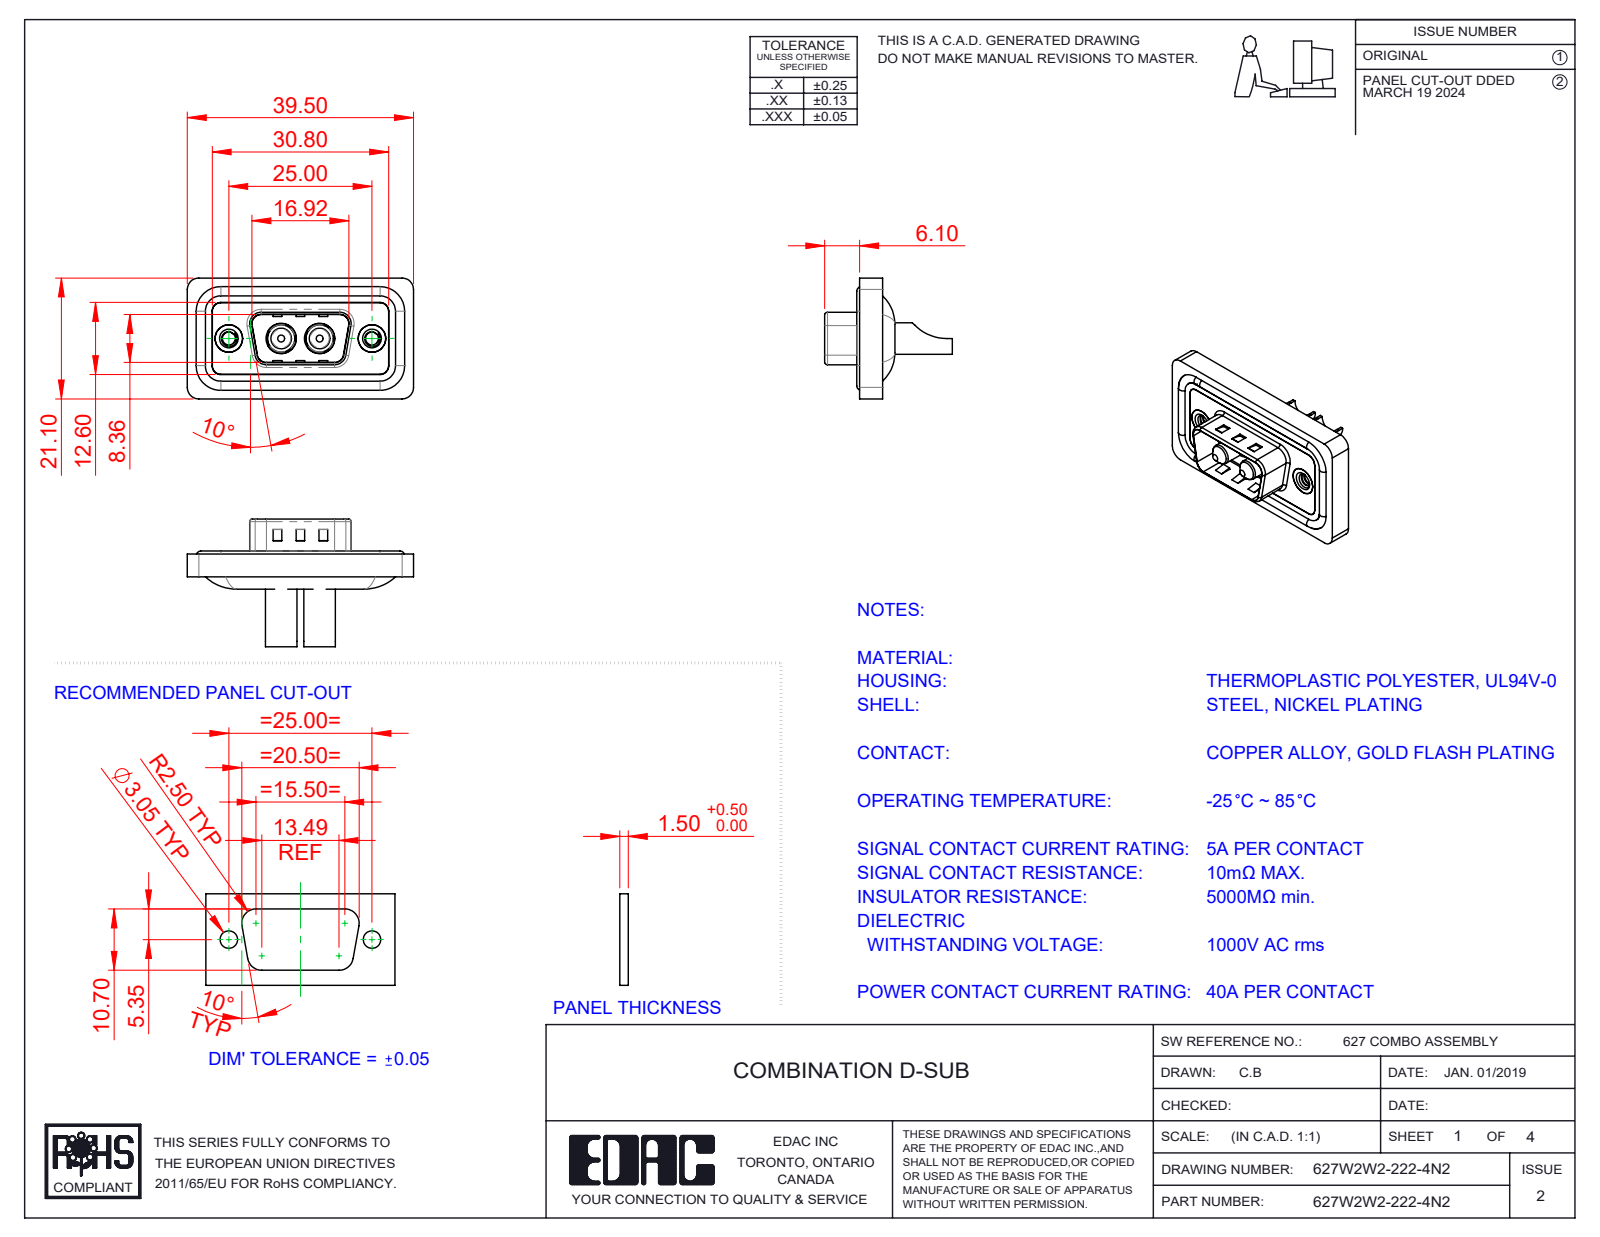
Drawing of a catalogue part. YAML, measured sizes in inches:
part_name: "627Combo Shell Rear_09 Contacts; 627Combo Threaded Rivet_2; 627Combo Waterproof Housing_09 Contacts; 627Combo Shell Front_09 Contacts (+3 more)"
step_written_by: "SolidWorks 2023 (CONFIG_CONTROL_DESIGN)"
units: inches
bodies: {solids: 11, faces: 497, planar: 169, cylindrical: 220, other: 108}
overall_size: [1.555, 0.878, 0.831]
volume: 0.277
surface_area: 11.26
round_holes:
  - {diameter: 0.089, count: 2}
  - {diameter: 0.157, count: 2}
  - {diameter: 0.181, count: 2}
  - {diameter: 0.189, count: 2}
  - {diameter: 0.191, count: 2}
  - {diameter: 0.197, count: 2}
  - {diameter: 0.209, count: 2}
round_bosses_or_shafts:
  - {diameter: 0.063, count: 4}
  - {diameter: 0.217, count: 2}
  - {diameter: 0.205, count: 2}
  - {diameter: 0.193, count: 2}
  - {diameter: 0.187, count: 2}
  - {diameter: 0.148, count: 2}
  - {diameter: 0.142, count: 2}
partial_cylinders:
  - {radius: 0.059, count: 22}
  - {radius: 0.079, count: 18}
  - {radius: 0.02, count: 8}
  - {radius: 0.063, count: 8}
  - {radius: 0.01, count: 4}
  - {radius: 0.024, count: 4}
  - {radius: 0.026, count: 4}
  - {radius: 0.035, count: 4}
face_to_face_distances: [0.016, 0.043, 0.114, 0.122, 0.02, 0.063, 0.059, 0.098, 0.028, 0.157]
hole_center_spacings: [0.36, 0.624, 0.265, 0.984]
